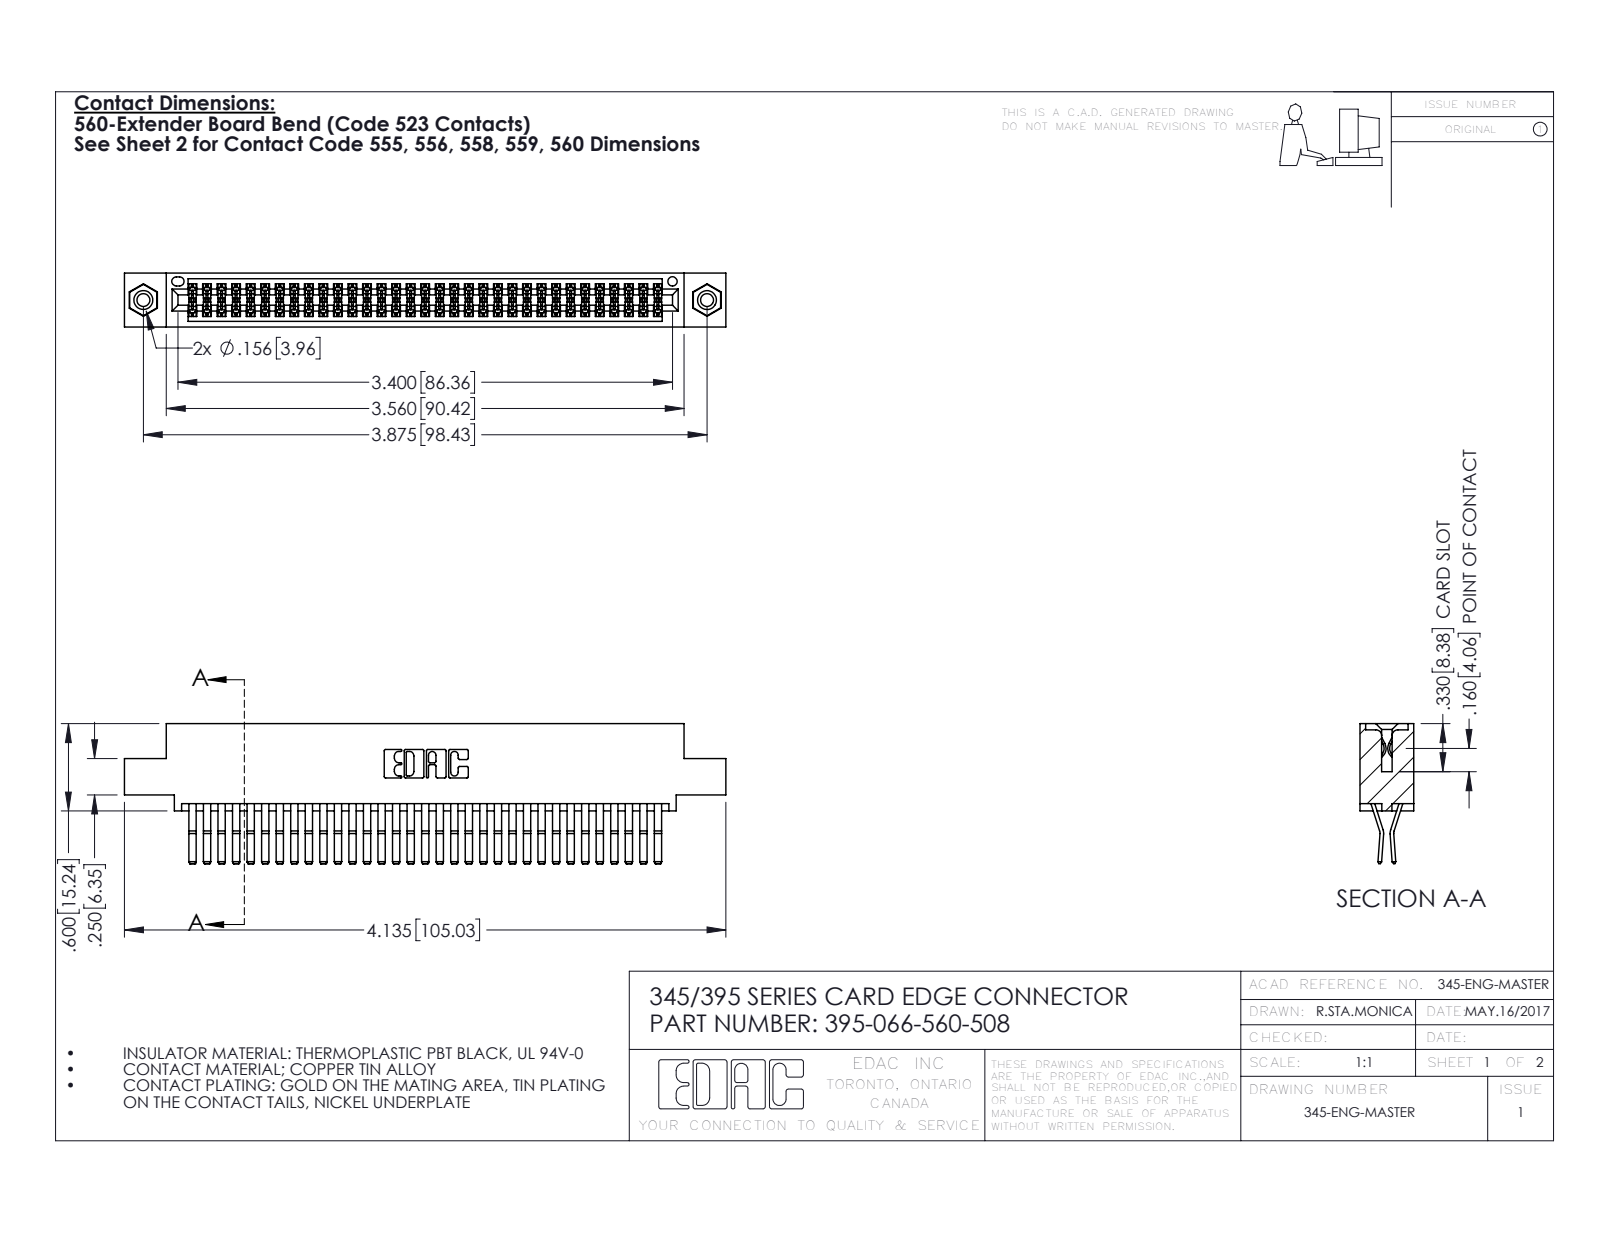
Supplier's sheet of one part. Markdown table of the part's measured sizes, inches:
| quantity | value |
| --- | --- |
| part name | 345 Part_0.110 Offset - 0.156 Dia-TI; 345-250-001_345-250-003-102; 345-292-001_560 Tail; 395-066-560-508 |
| STEP written by | SolidWorks 2016 (CONFIG_CONTROL_DESIGN) |
| units | inches |
| bodies | 69 solids, 3622 faces (2294 planar, 1312 cylindrical, 16 other) |
| overall size | 4.135 × 0.962 × 0.37 |
| volume | 0.639 in³ |
| surface area | 25.61 in² |
| round holes (diameter × count) | 0.089 × 2, 0.125 × 2, 0.156 × 2, 0.064 × 1 |
| round bosses / shafts (diameter × count) | 0.155 × 2 |
| partial cylindrical surfaces (radius × count) | 0.006 × 100, 0.01 × 22, 0.007 × 6, 0.031 × 6, 0.026 × 3, 0.01 × 2, 0.014 × 2, 0.019 × 2 |
| main face-to-face distances | 0.025, 0.072, 0.298, 0.2, 0.37, 0.098, 0.272, 0.225, 0.175, 0.149 |
| hole center spacings | 0.27, 3.64, 3.875 |
